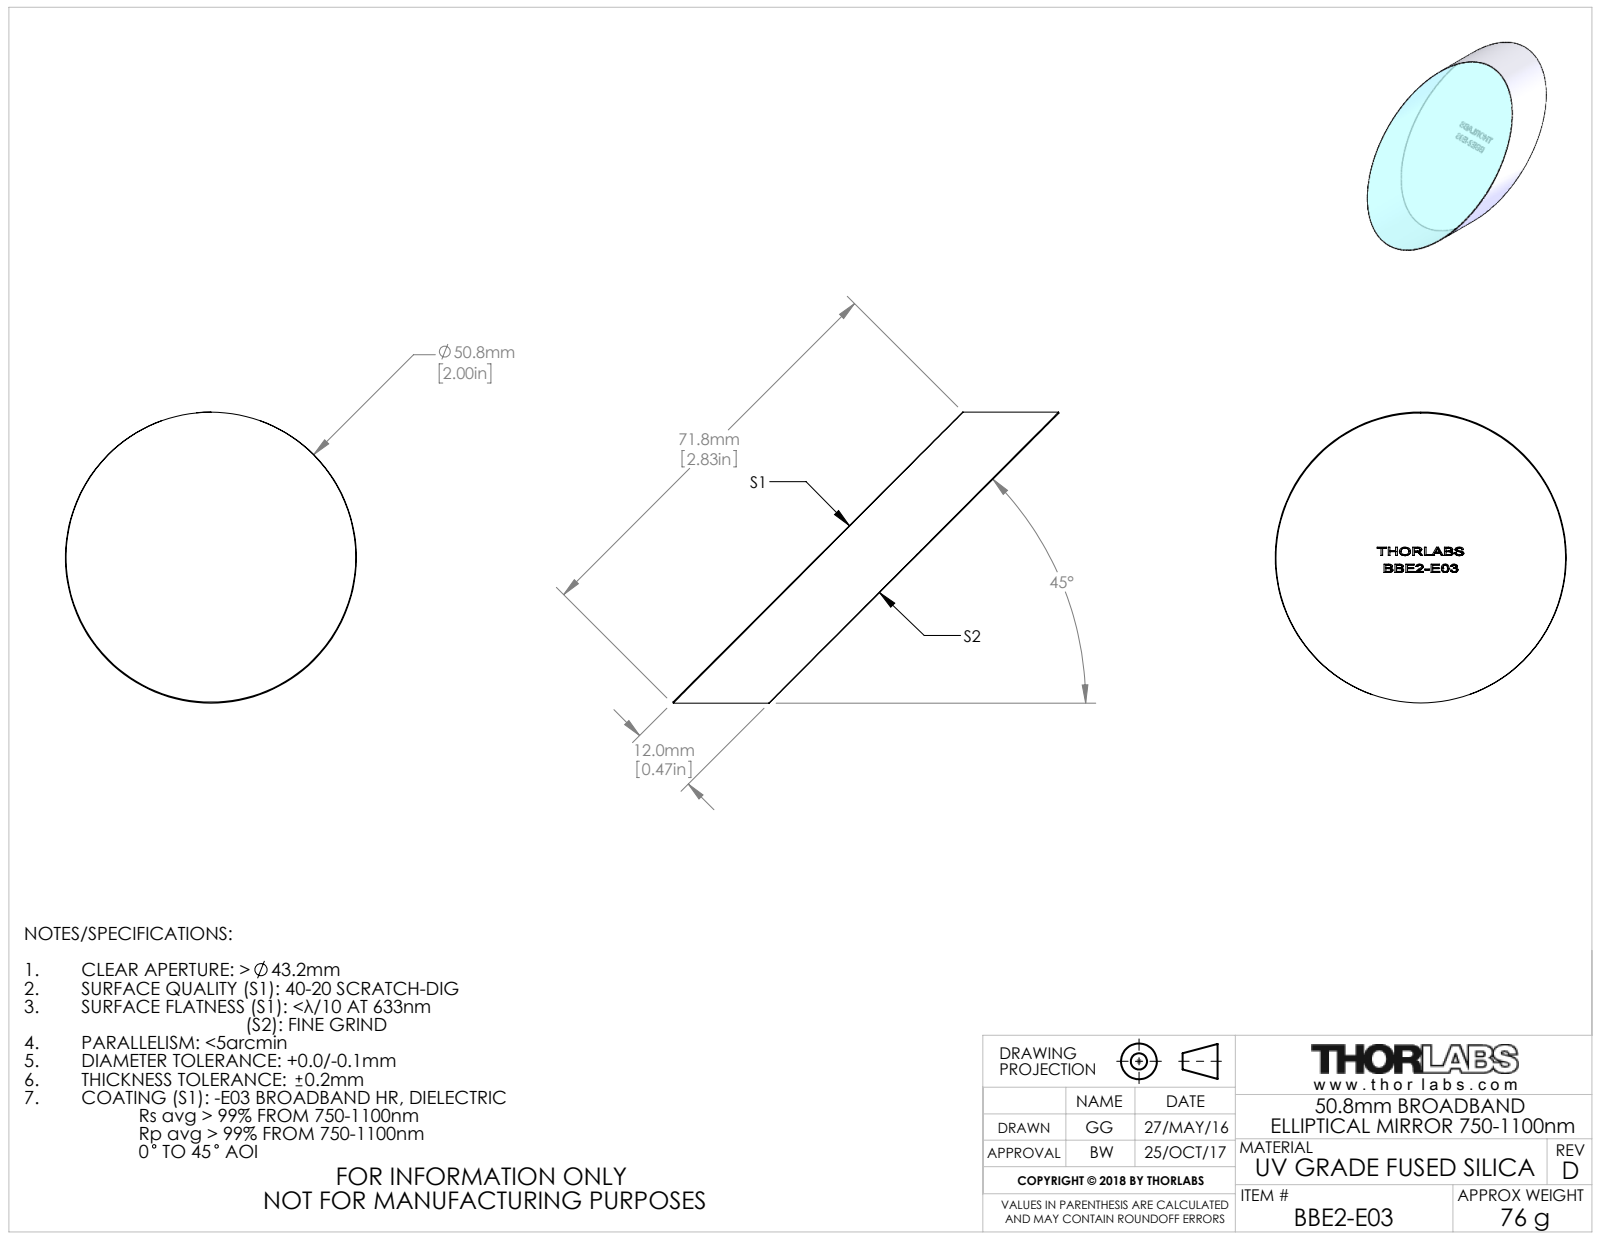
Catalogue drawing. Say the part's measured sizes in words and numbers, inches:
The part is named "21940-E0W". Its 3-D file was written by "SolidWorks 2016 (CONFIG_CONTROL_DESIGN)". It is 1 solid with 241 faces: 140 planar, 2 cylindrical and 99 other. Overall it measures 2.654 by 2 by 2 inches. Its volume is 2.099 cubic inches and its surface area 13.02 square inches. Round bosses or shafts: 1 of diameter 2. The main face-to-face distances are 0.472, 0.164, 0.081, 0.034, 0.244, 0.046, 0.117, 0.218, 0.062, 0.198.
